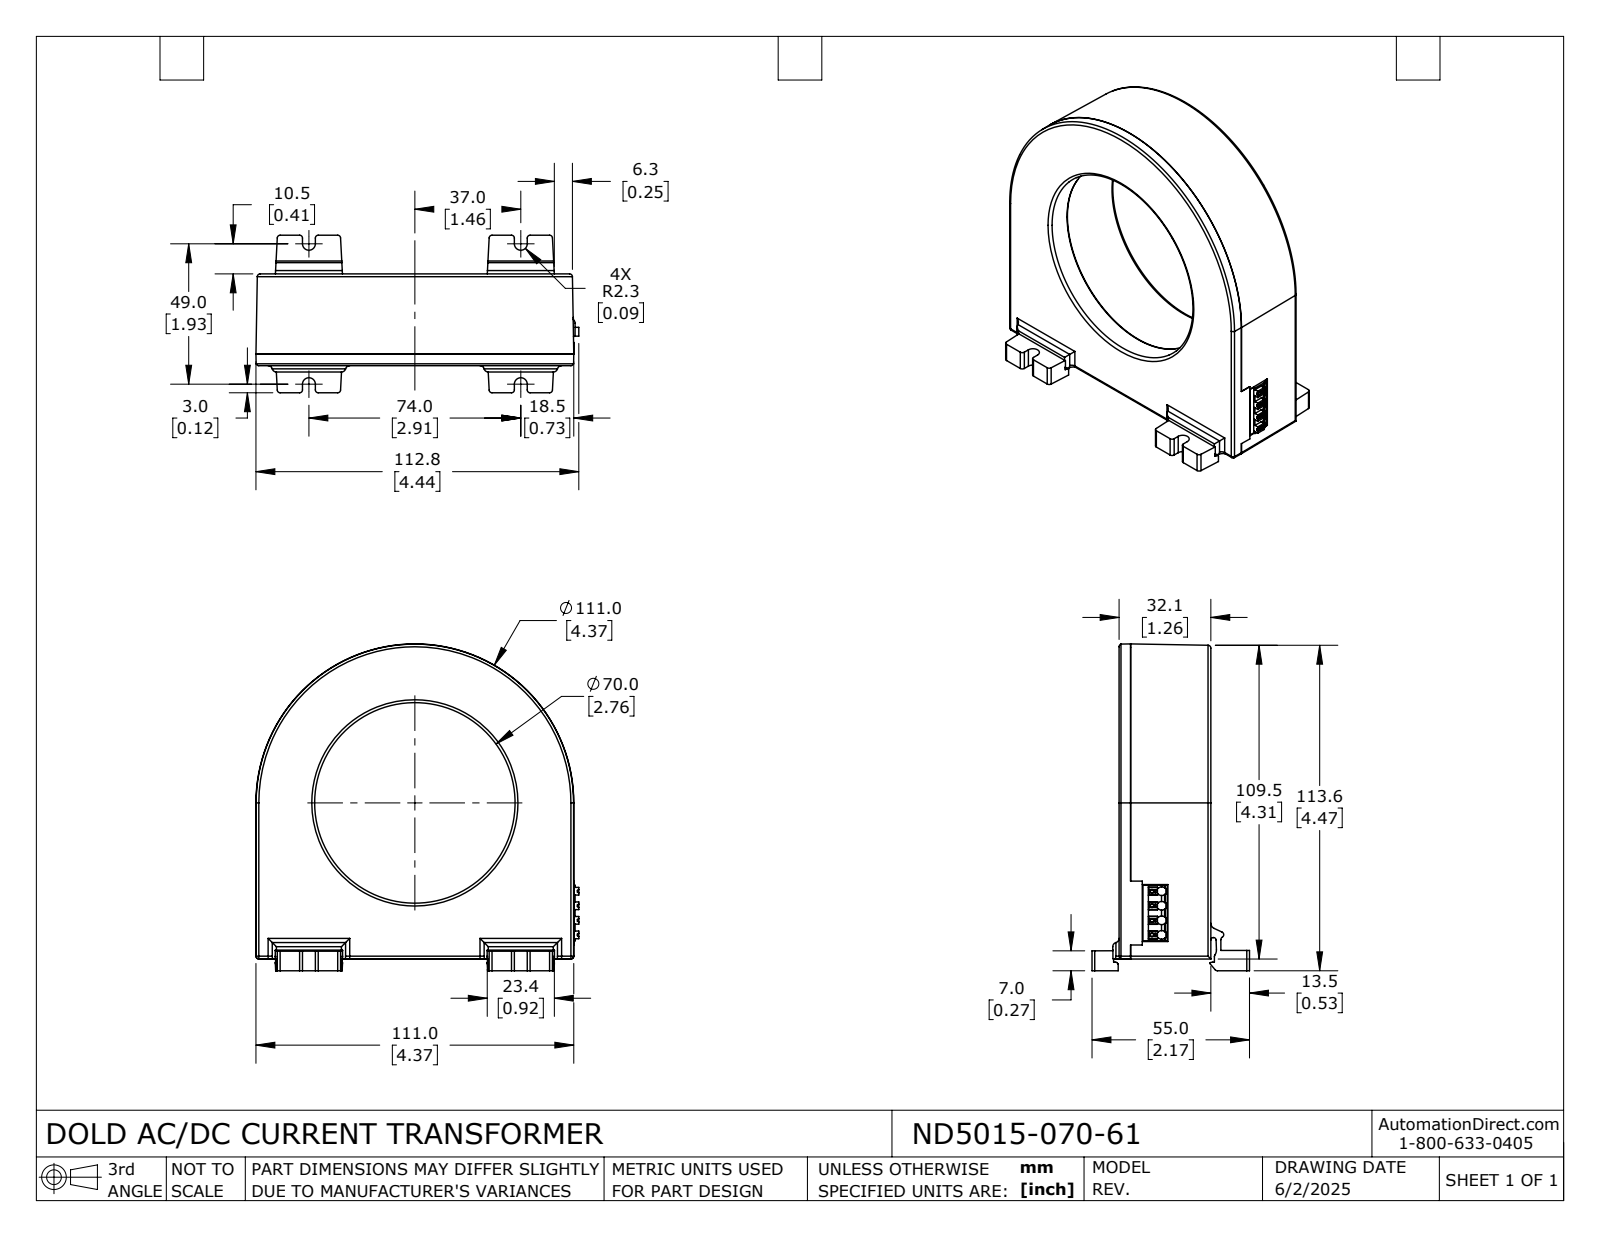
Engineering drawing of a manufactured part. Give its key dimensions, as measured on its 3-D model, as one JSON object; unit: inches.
{"part_name": "ND5015-070-61", "step_written_by": "SolidWorks 2024 (AUTOMOTIVE_DESIGN)", "units": "inches", "bodies": {"solids": 1, "faces": 395, "planar": 254, "cylindrical": 112, "other": 29}, "overall_size": [4.492, 4.439, 2.165], "volume_in3": 13.96, "surface_area_in2": 75.69, "round_holes": [[0.047, 4], [2.756, 1], [2.907, 1], [2.925, 1]], "partial_cylinders_radius": [[0.039, 35], [0.059, 11], [0.071, 8], [0.089, 4], [0.012, 2], [0.02, 2], [0.035, 2], [0.01, 1]], "face_to_face_distances": [1.262, 0.161, 0.159, 1.102, 1.104, 0.157, 0.076, 0.118, 0.28, 2.911], "hole_center_spacings": [0.2, 0.4, 0.6]}
